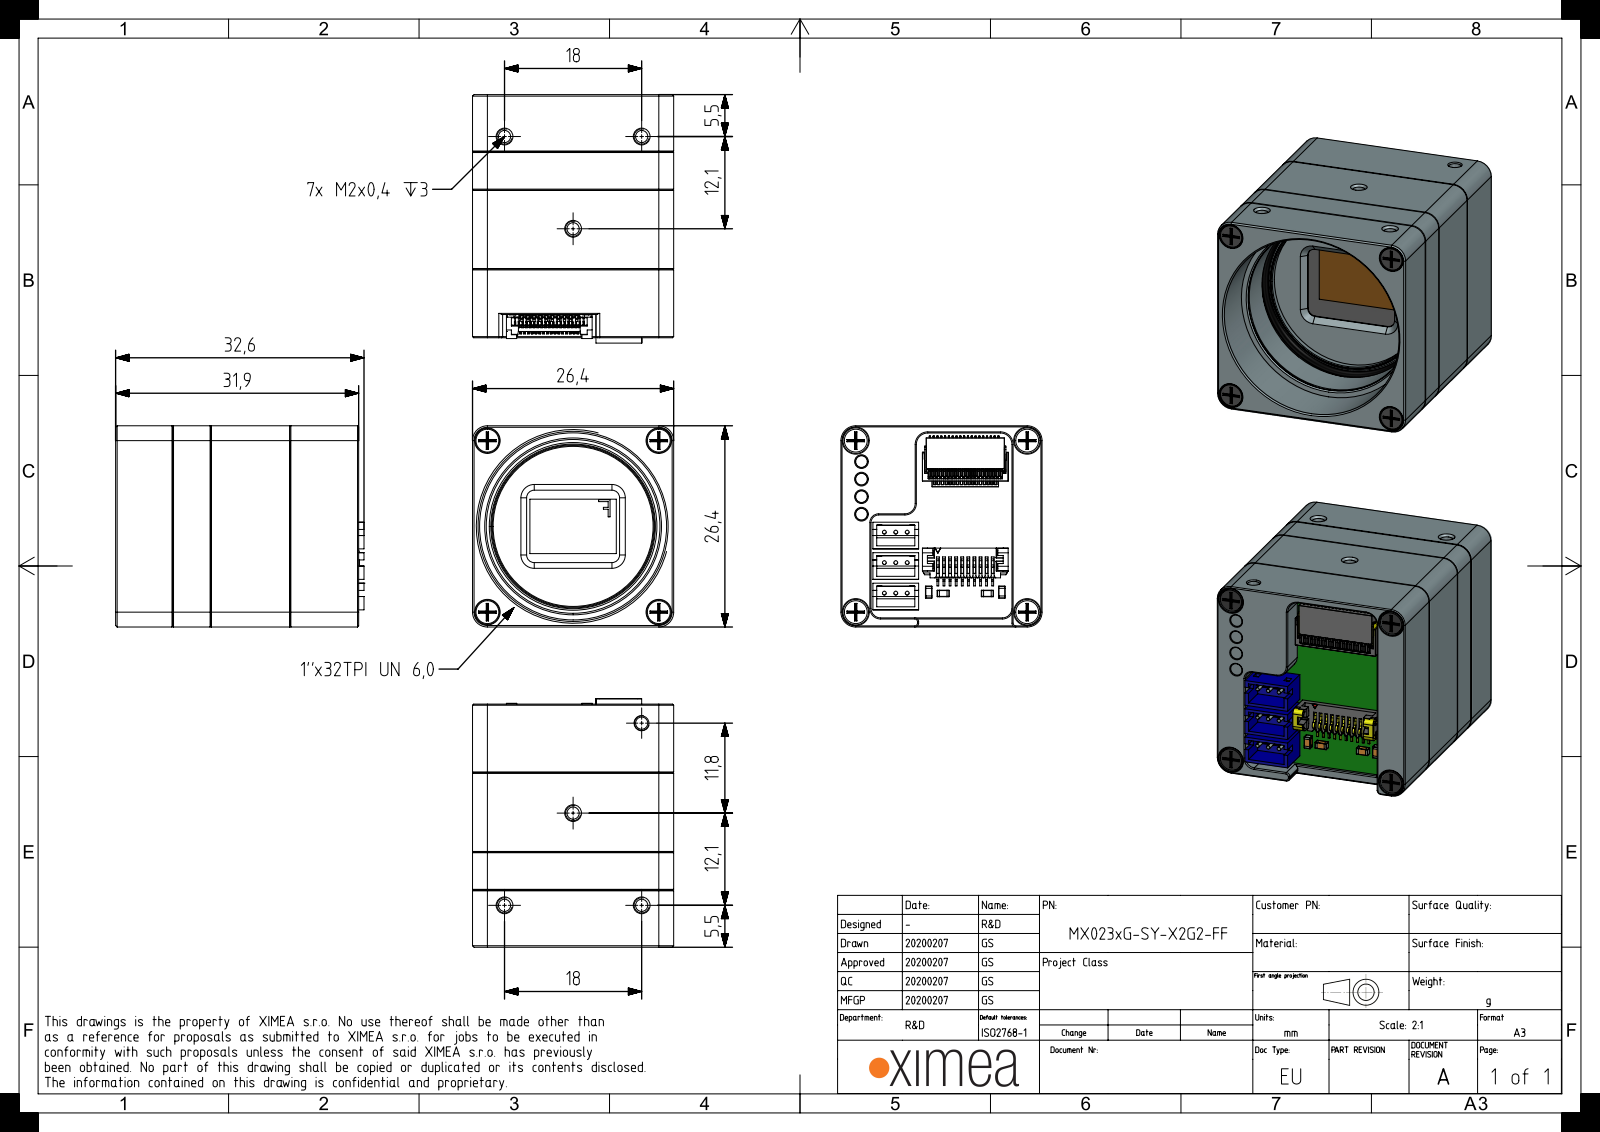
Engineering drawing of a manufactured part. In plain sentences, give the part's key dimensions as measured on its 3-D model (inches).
The part is named "MX-X2G2-MAIN-FF-PCA-REV2; MECH-THERM-PAD-10X5X1; SROB-M2x4-CUST; MX-X2G2-CONN-FF-PCA (+8 more)". Its 3-D file was written by "SIEMENS PLM Software NX 1907 (AUTOMOTIVE_DESIGN)". It is 424 solids with 23994 faces: 14227 planar, 6768 cylindrical and 2999 other. Overall it measures 1.283 by 1.039 by 1.039 inches. Its volume is 0.706 cubic inches and its surface area 36.51 square inches. Round holes: 16 of diameter 0.063, 9 of diameter 0.028, 8 of diameter 0.079, 4 of diameter 0.035, 4 of diameter 0.035, 4 of diameter 0.071, 4 of diameter 0.083, 4 of diameter 0.118, 4 of diameter 0.126, 4 of diameter 0.132, 3 of diameter 0.012, 2 of diameter 0.024. Round bosses or shafts: 9 of diameter 0.02, 8 of diameter 0.075, 6 of diameter 0.118, 4 of diameter 0.064, 4 of diameter 0.033, 2 of diameter 0.063, 2 of diameter 0.031, 1 of diameter 0.984. Partial cylindrical surfaces (rounded edges, fillets, slot ends): 77 of radius 0.004, 74 of radius 0.005, 30 of radius 0.006, 30 of radius 0.013, 27 of radius 0.015, 22 of radius 0.059, 18 of radius 0.039, 16 of radius 0.051. The main face-to-face distances are 0.039, 0.142, 1.039, 0.272, 0.181, 0.224, 0.413, 0.453, 0.189, 0.102. The hole center spacings are 0.626, 0.059, 0.15, 0.168, 0.508, 0.515, 0.717, 0.739.
